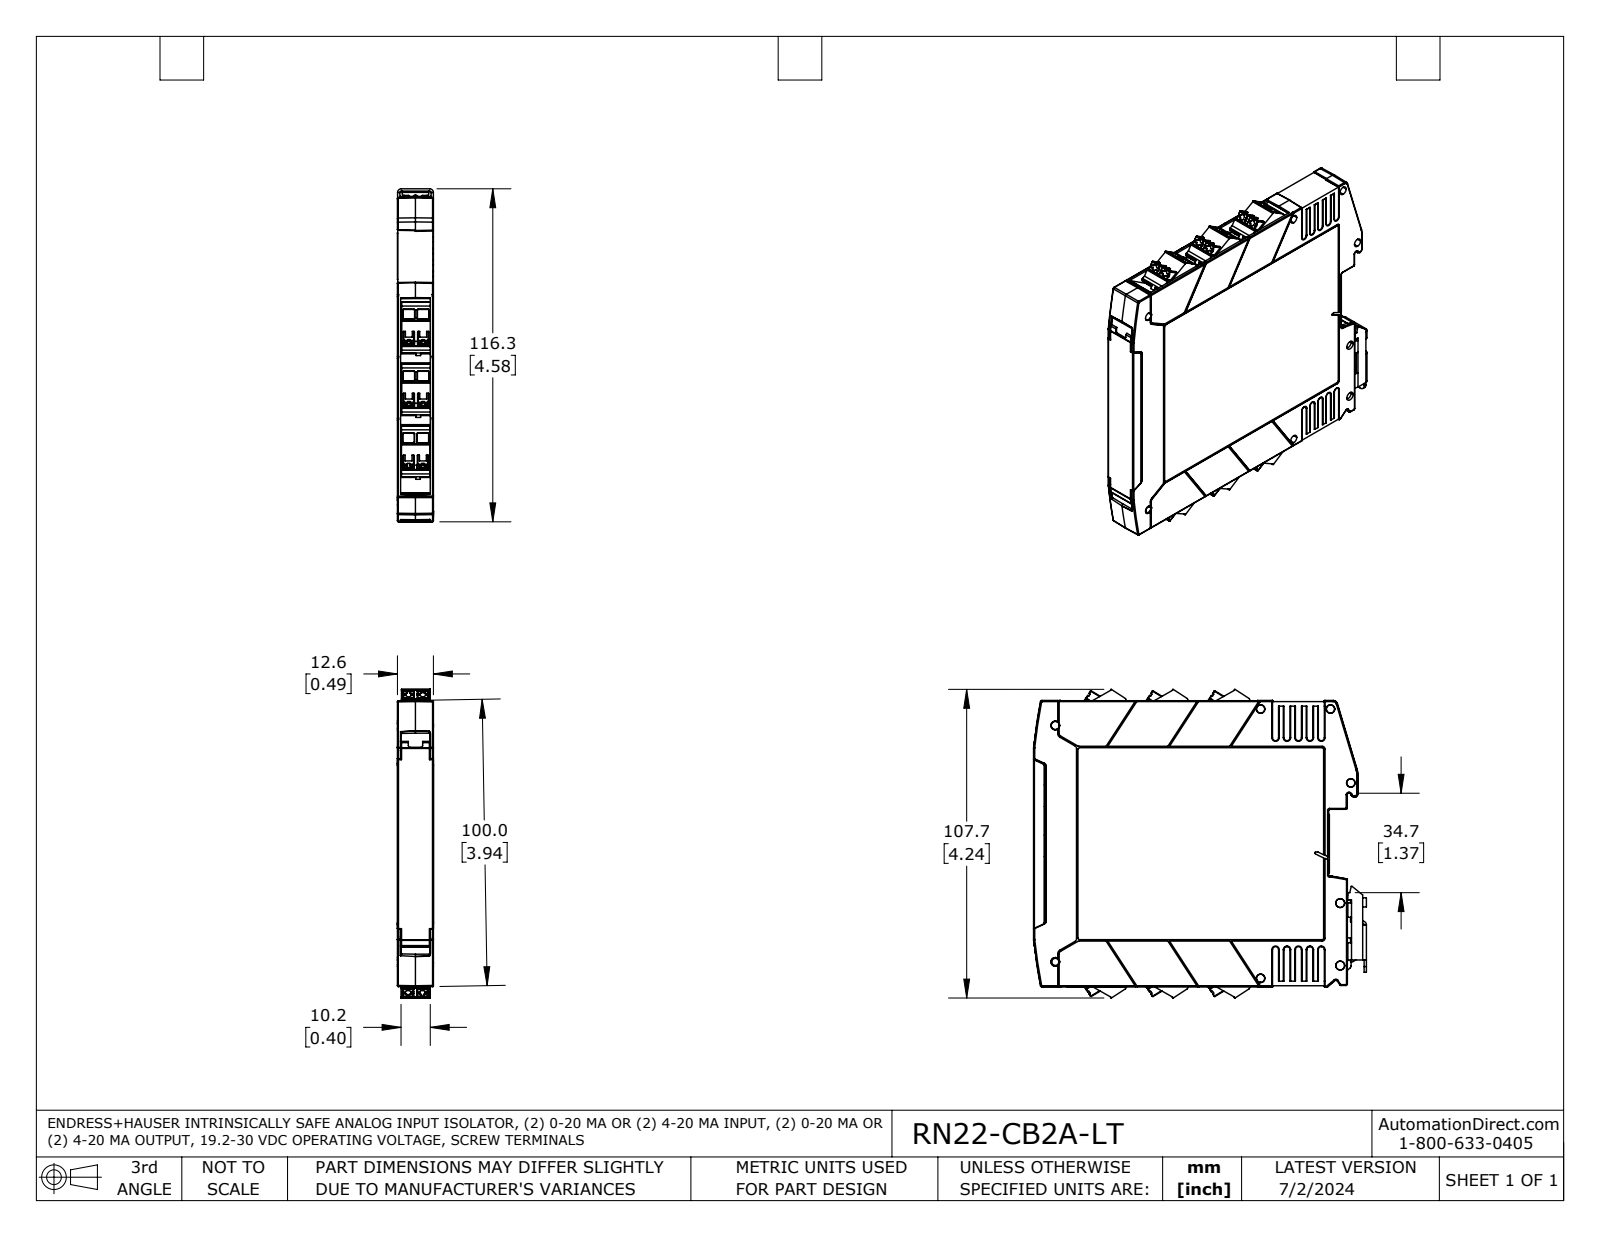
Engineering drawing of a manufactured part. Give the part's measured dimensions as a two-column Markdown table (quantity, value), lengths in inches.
| quantity | value |
| --- | --- |
| part name | RN22-CB2A-LT |
| STEP written by | SolidWorks 2021 (AUTOMOTIVE_DESIGN) |
| units | inches |
| bodies | 2 solids, 3045 faces (1939 planar, 765 cylindrical, 341 other) |
| overall size | 4.577 × 4.242 × 0.496 |
| volume | 7.84 in³ |
| surface area | 58.97 in² |
| round holes (diameter × count) | 0.118 × 3, 0.009 × 2, 0.097 × 1, 0.111 × 1 |
| partial cylindrical surfaces (radius × count) | 0.008 × 149, 0.02 × 71, 0.012 × 66, 0.039 × 28, 0.005 × 16, 0.114 × 12, 0.009 × 10, 0.024 × 10 |
| main face-to-face distances | 0.494, 0.043, 0.451, 0.039, 0.447, 0.047, 0.491, 0.435, 0.392, 0.031 |
| hole center spacings | 2.832, 4.477, 0.759, 0.76, 0.961, 2.073, 2.074, 3.031 |
